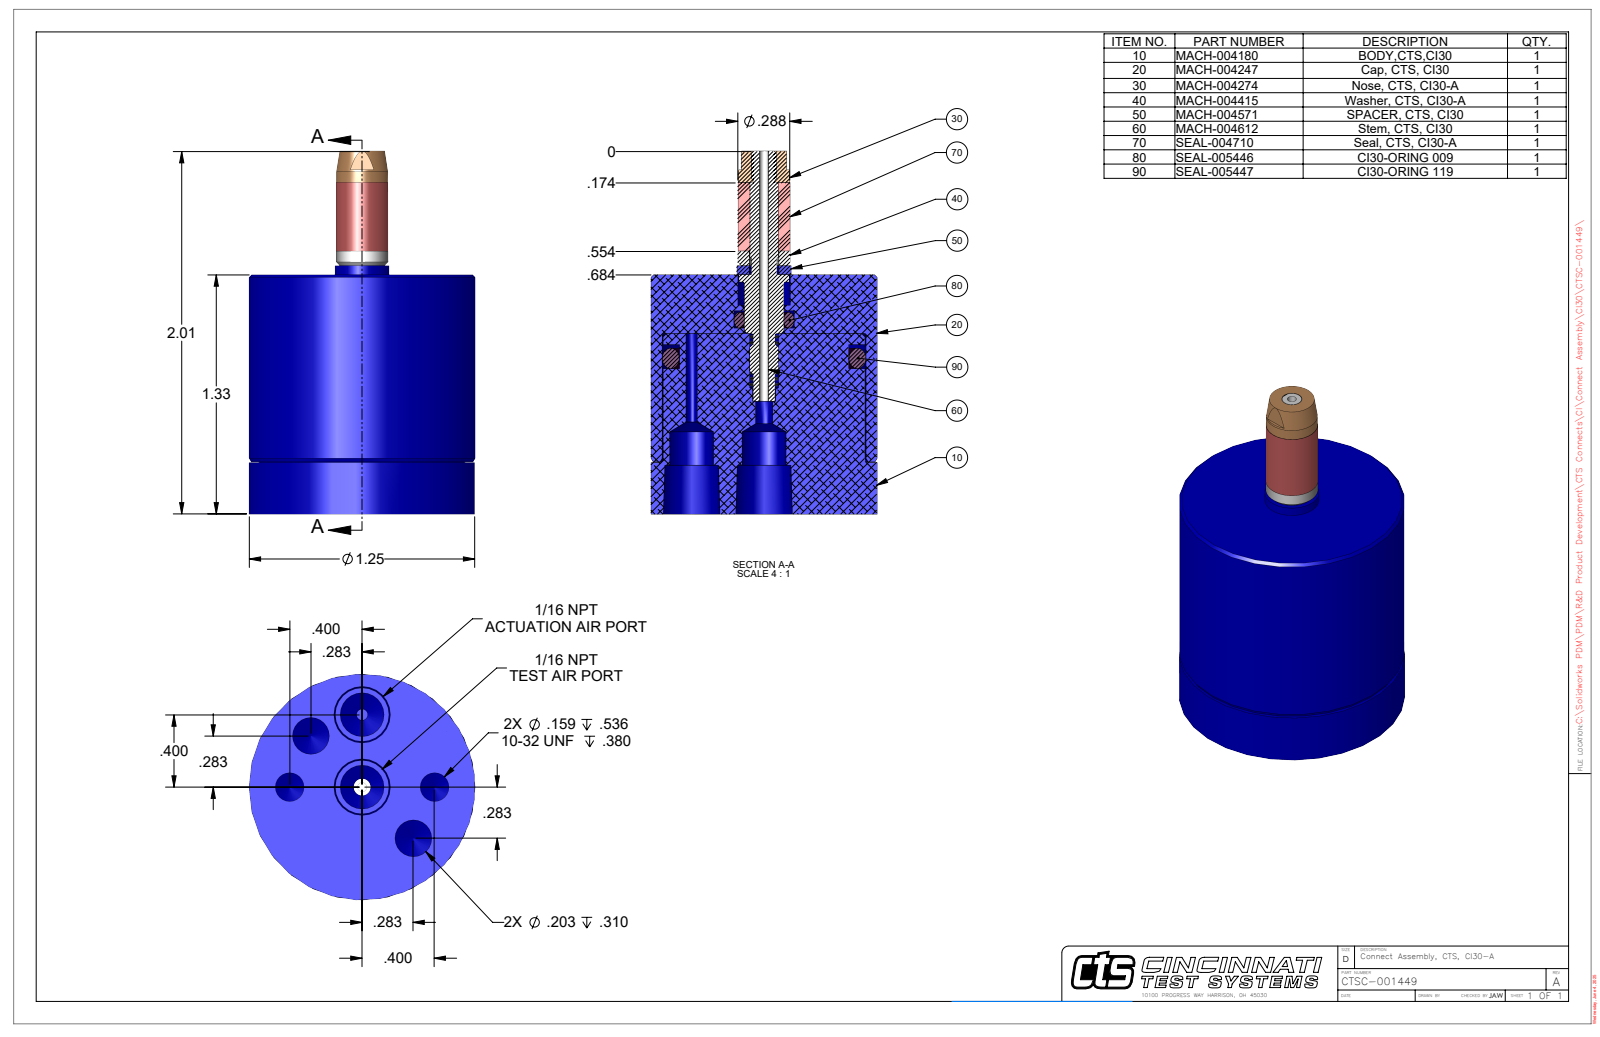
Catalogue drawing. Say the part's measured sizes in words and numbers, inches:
The part is named "CTSC-001449". Its 3-D file was written by "SolidWorks 2023 (AUTOMOTIVE_DESIGN)". It is 2 solids with 81 faces: 20 planar, 36 cylindrical and 25 other. Overall it measures 2.009 by 1.25 by 1.25 inches. Its volume is 1.56 cubic inches and its surface area 12.2 square inches. Round holes: 2 of diameter 0.159, 2 of diameter 0.203, 2 of diameter 0.242, 1 of diameter 0.052, 1 of diameter 0.062, 1 of diameter 0.094, 1 of diameter 0.289, 1 of diameter 1.125. Round bosses or shafts: 1 of diameter 1.25, 1 of diameter 1.115, 1 of diameter 0.3, 1 of diameter 0.288, 1 of diameter 0.285, 1 of diameter 0.277. The main face-to-face distances are 1.325, 1.039, 0.287, 0.29, 1.035, 0.52, 0.233, 0.23, 0.806, 0.015. The hole center spacings are 0.306, 0.4, 0.739, 0.4, 0.566, 0.8, 0.8.
